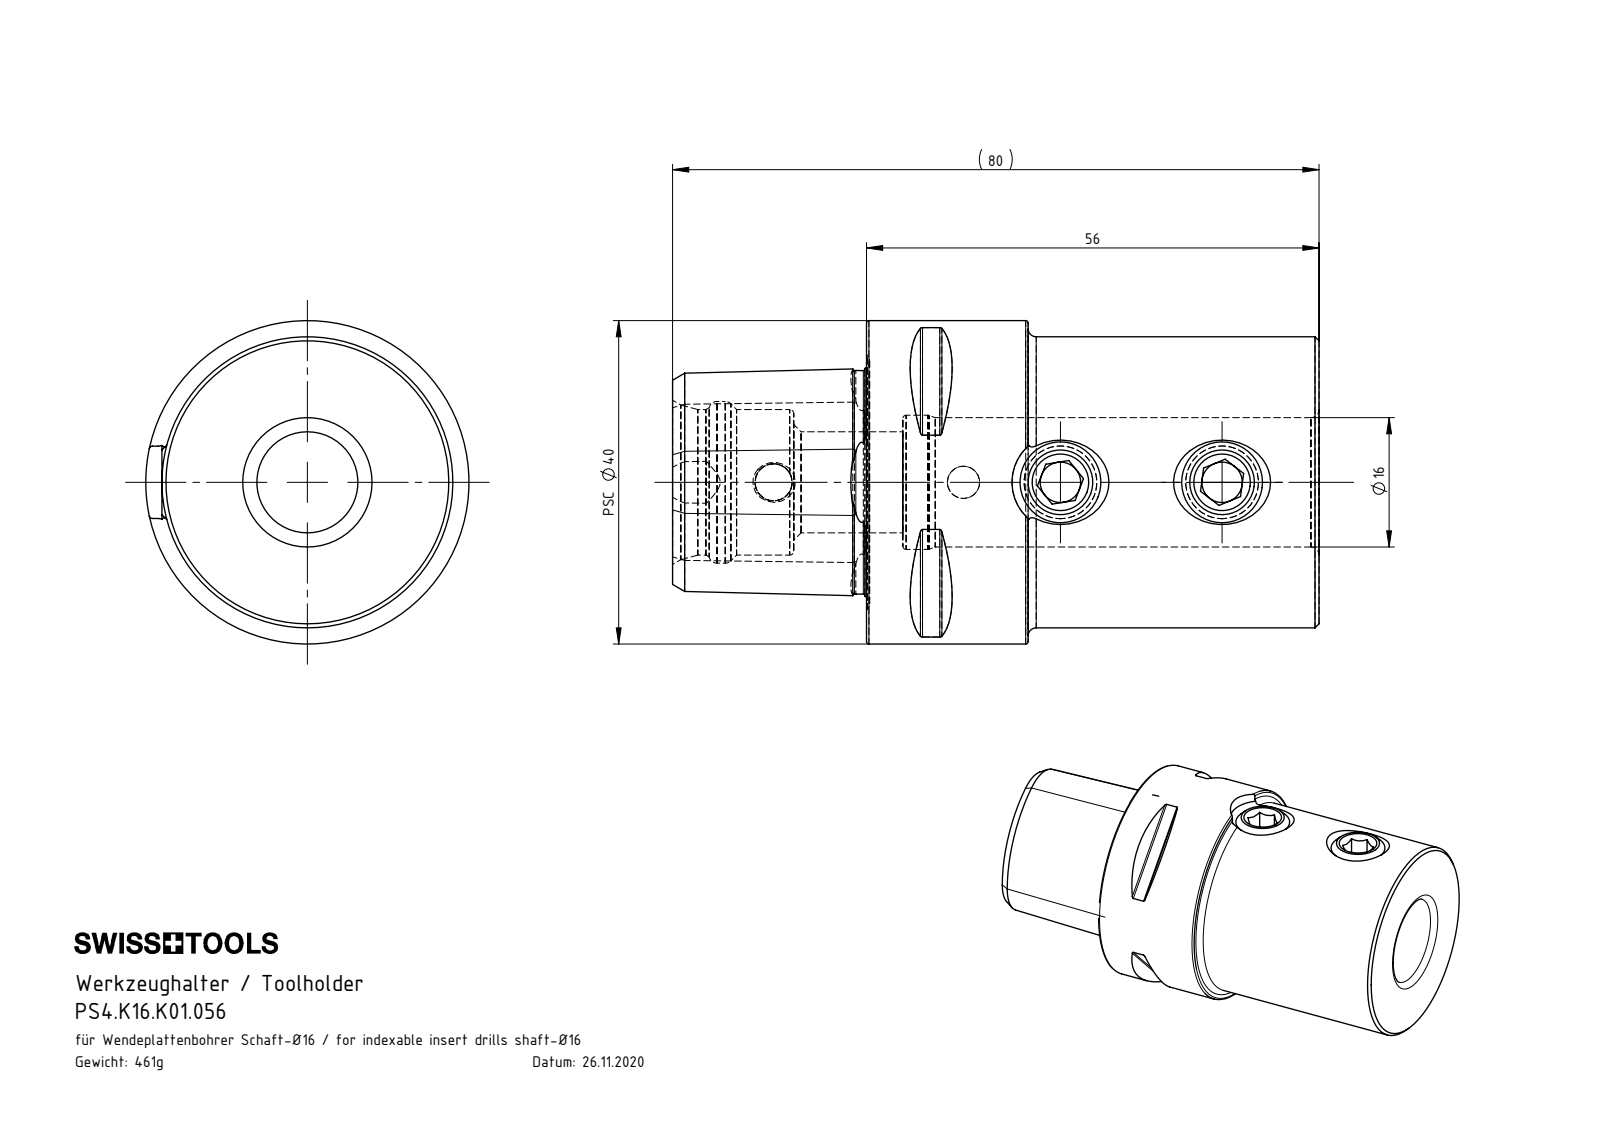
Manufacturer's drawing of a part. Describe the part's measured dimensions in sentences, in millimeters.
The part is named "PS4-K16.K01.056_A; K16-ER1.010.010_A_PreviewCfg; PS4.K16.K01.056". Its 3-D file was written by "SolidWorks 2022 (AUTOMOTIVE_DESIGN)". It is 3 solids with 211 faces: 49 planar, 44 cylindrical and 118 other. Overall it measures 80 by 40 by 40 millimeters. Its volume is 58 716 cubic millimeters and its surface area 16 272 square millimeters. Round holes: 2 of diameter 5, 2 of diameter 9, 1 of diameter 4, 1 of diameter 4.6, 1 of diameter 12.5, 1 of diameter 16, 1 of diameter 16.6, 1 of diameter 18, 1 of diameter 20. Round bosses or shafts: 2 of diameter 10, 1 of diameter 40, 1 of diameter 36. Partial cylindrical surfaces (rounded edges, fillets, slot ends): 8 of radius 0.3, 1 of radius 3, 1 of radius 6. The main face-to-face distances are 56, 24, 80, 15.52, 35.3, 44, 20, 36, 4.5, 28.5. The hole center spacings are 12, 20, 23.5, 32, 35.5, 55.5.
